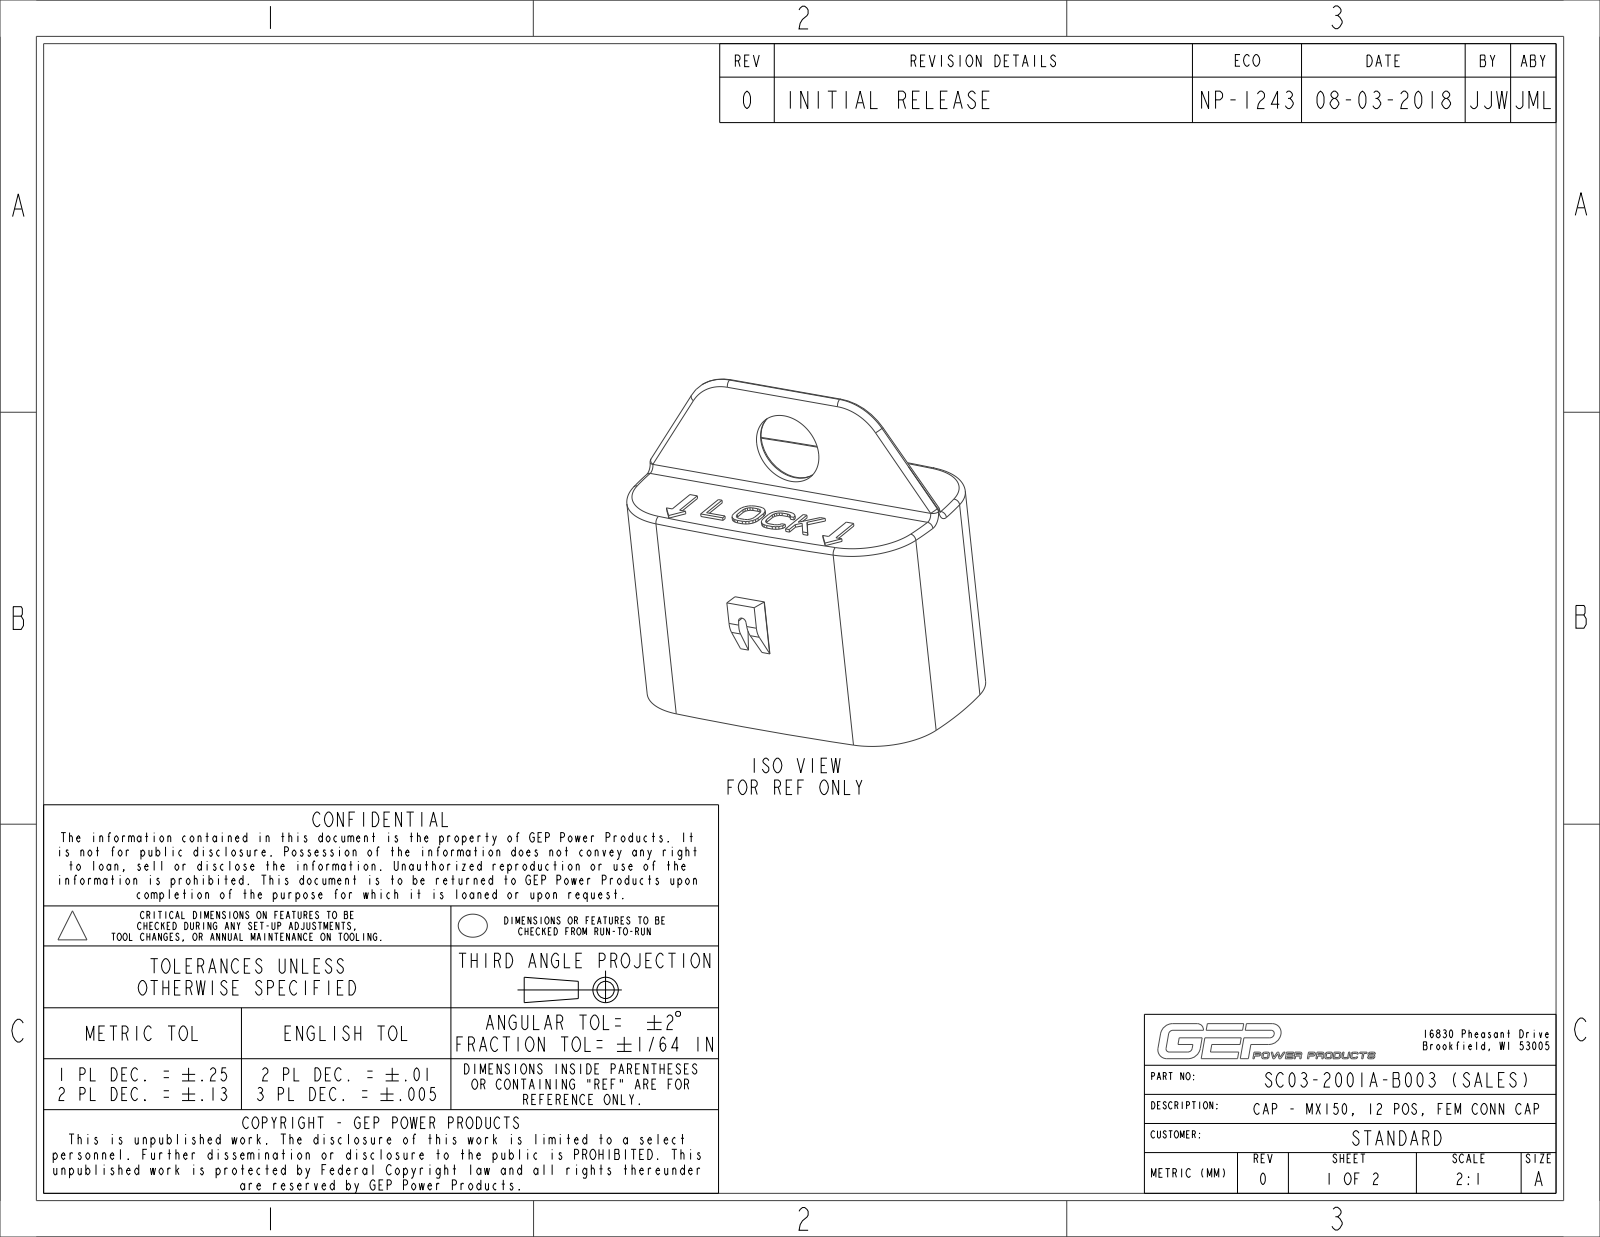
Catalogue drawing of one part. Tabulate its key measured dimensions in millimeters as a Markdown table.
| quantity | value |
| --- | --- |
| part name | PC03-2001A-B003_NCF; SC03-2001A-B003_NCF_ASM |
| STEP written by | CREO PARAMETRIC BY PTC INC, 2017110 (CONFIG_CONTROL_DESIGN) |
| units | millimeters |
| bodies | 1 solid, 438 faces (259 planar, 33 cylindrical, 146 other) |
| overall size | 29.44 × 29 × 19.47 |
| volume | 2 570 mm³ |
| surface area | 4 324 mm² |
| round holes (diameter × count) | 3 × 1, 6.35 × 1 |
| partial cylindrical surfaces (radius × count) | 5.72 × 4, 0.5 × 3, 0.3 × 2, 0.6 × 2, 31.73 × 2, 203.79 × 2, 0.38 × 1, 2 × 1 |
| main face-to-face distances | 1, 18, 19, 0.85, 18.15, 1.25, 19.25, 1.1, 18.25, 0.75 |
